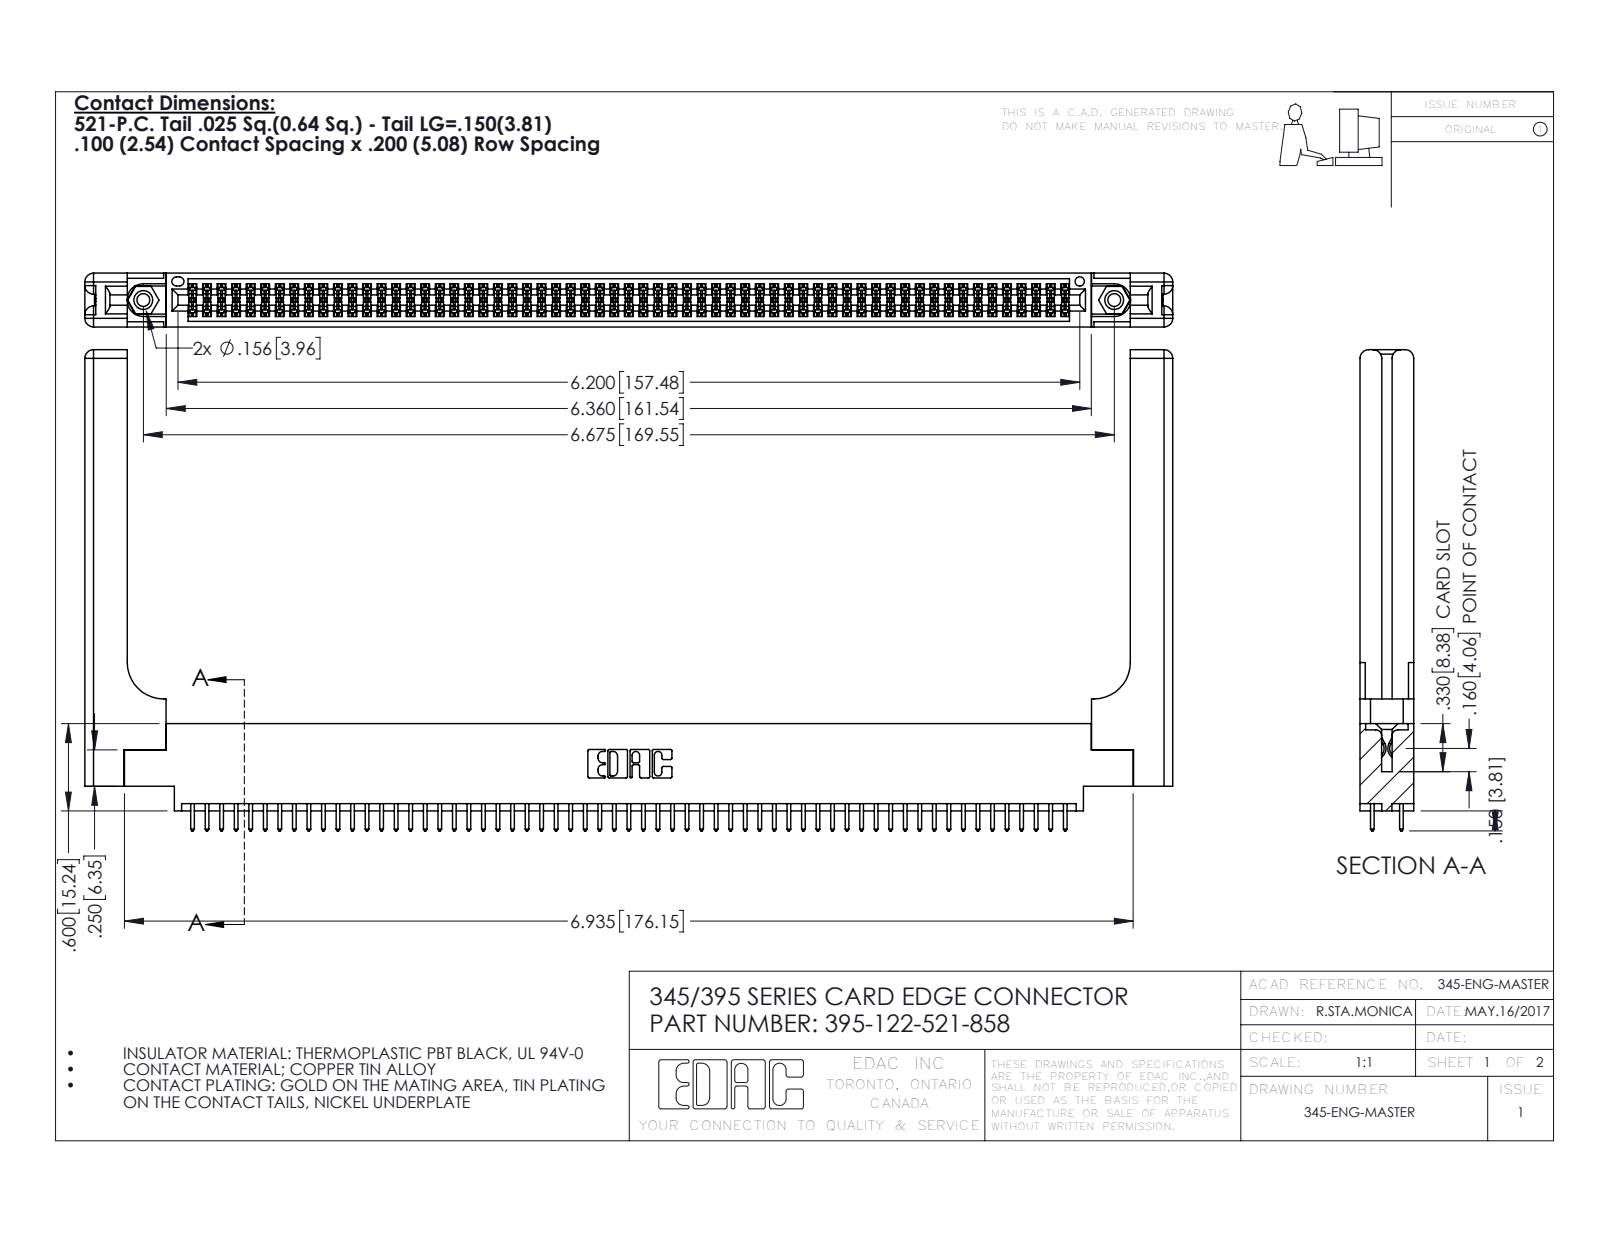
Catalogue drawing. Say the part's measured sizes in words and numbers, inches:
The part is named "345-292-001_345-293-121; 345-250-001_345-250-001-102; 395-122-521-858; 345 Part_0.170 Offset - 0.156 Dia-TH (+1 more)". Its 3-D file was written by "SolidWorks 2016 (CONFIG_CONTROL_DESIGN)". It is 127 solids with 6486 faces: 4258 planar, 2168 cylindrical and 60 other. Overall it measures 7.479 by 3.307 by 0.37 inches. Its volume is 1.644 cubic inches and its surface area 50.44 square inches. Round holes: 2 of diameter 0.089, 2 of diameter 0.125, 2 of diameter 0.156, 1 of diameter 0.064. Round bosses or shafts: 2 of diameter 0.155. Partial cylindrical surfaces (rounded edges, fillets, slot ends): 183 of radius 0.006, 122 of radius 0.01, 22 of radius 0.01, 16 of radius 0.06, 6 of radius 0.007, 6 of radius 0.031, 3 of radius 0.026, 2 of radius 0.014. The main face-to-face distances are 0.072, 0.298, 0.37, 0.098, 0.272, 0.025, 0.2, 0.225, 0.175, 0.148. The hole center spacings are 0.27, 6.439, 6.675.
